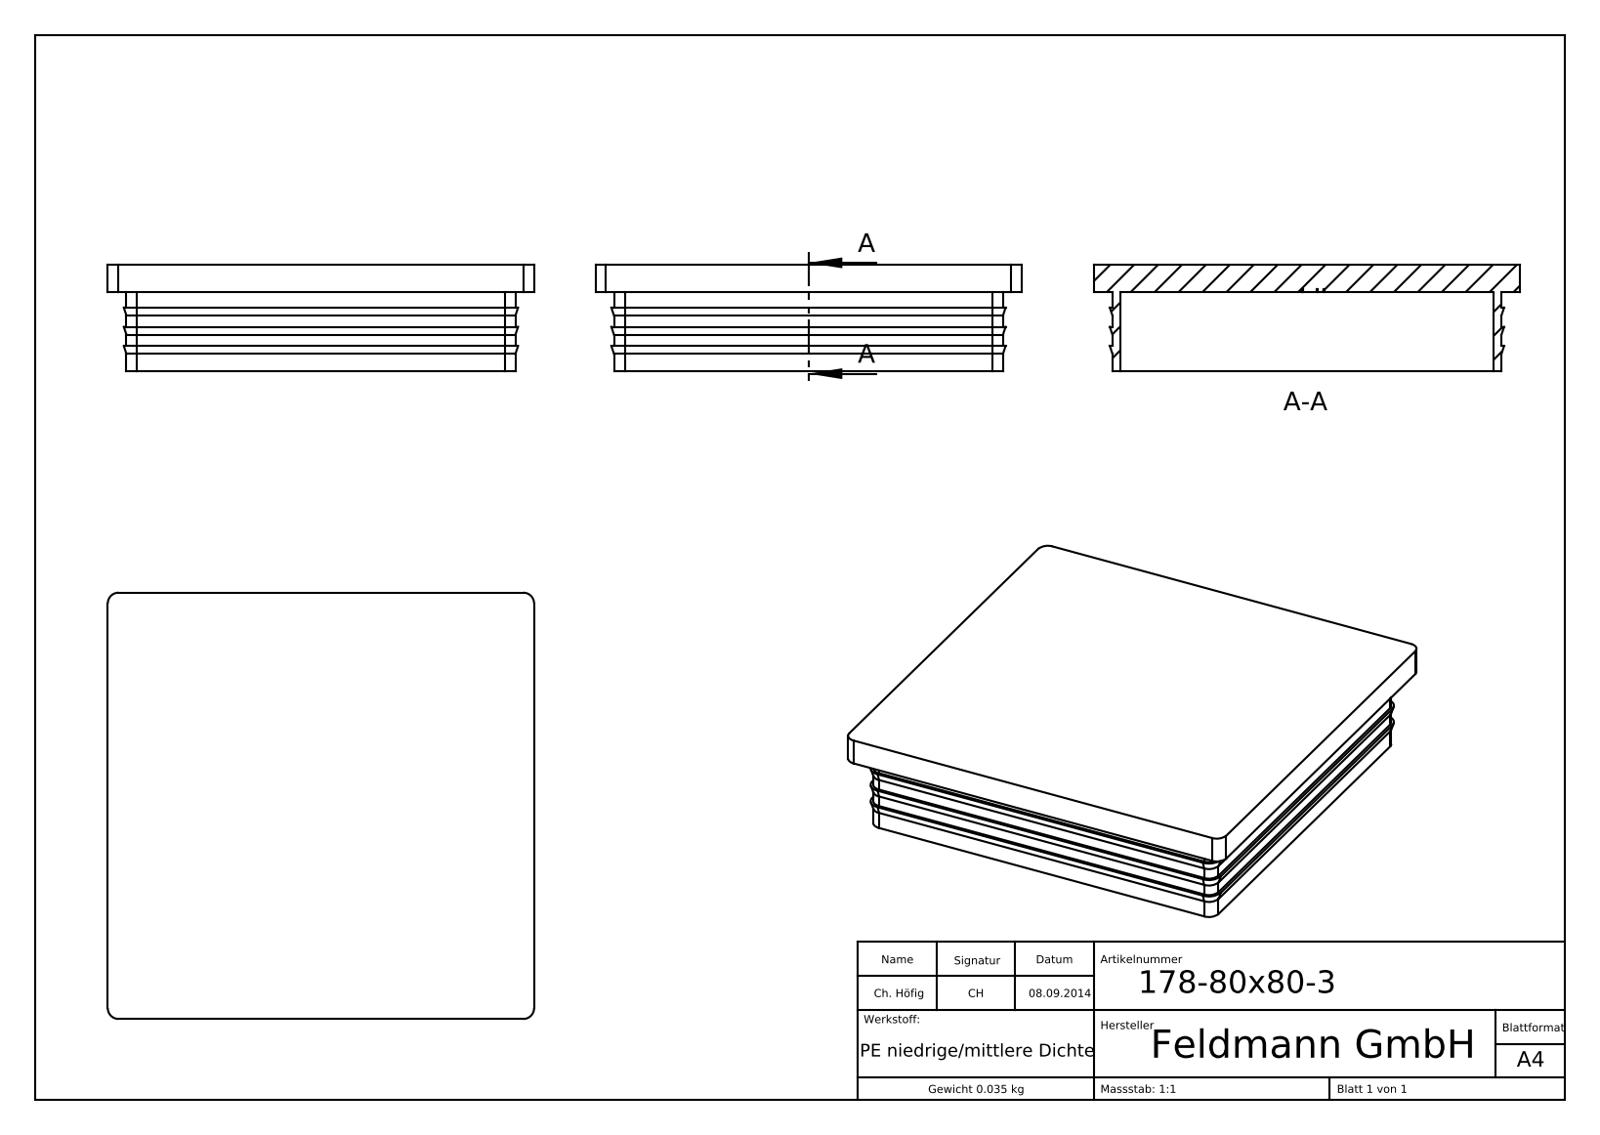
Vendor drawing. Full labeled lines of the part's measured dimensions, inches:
Part name (STEP PRODUCT): 178-80x80-3
STEP written by: SolidWorks 2015 (CONFIG_CONTROL_DESIGN)
Units: inches
Bodies: 1 solid, 325 faces (162 planar, 20 cylindrical, 143 other)
Overall size (bounding box): 3.15 × 3.15 × 0.787
Volume: 2.361 in³ · Surface area: 36.38 in²
Partial cylindrical surfaces — rounded edges, fillets, slot ends (radius × count): R0.079 ×8
Main face-to-face distances: 0.197, 0.059, 2.815, 2.756, 0.138, 2.953, 3.012, 2.874, 0.045, 3.15
